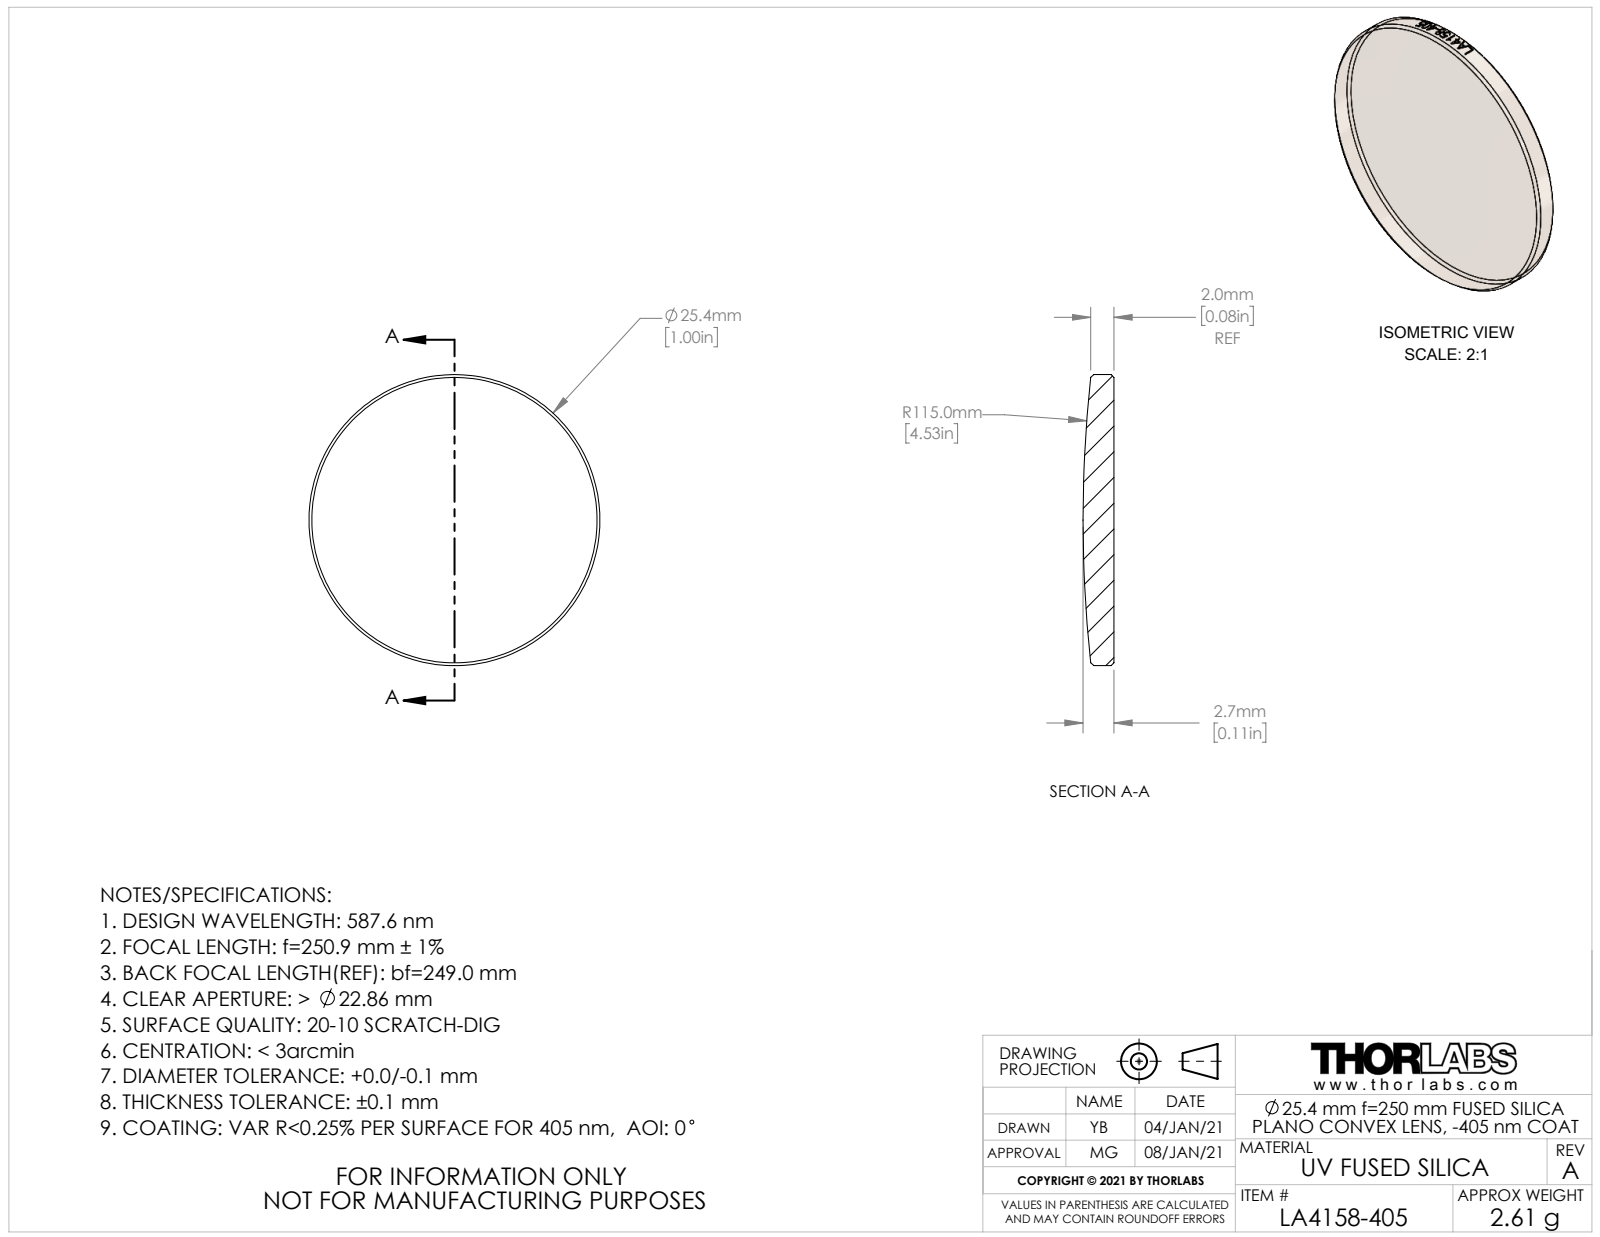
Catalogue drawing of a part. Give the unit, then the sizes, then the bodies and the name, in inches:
Units: inches
Overall size (bounding box): 1 × 1 × 0.106
Round bosses / shafts (diameter × count): ⌀1 ×1
Volume: 0.072 in³ · Surface area: 1.786 in²
Bodies: 1 solid, 30 faces (1 planar, 23 cylindrical, 6 other)
Part name (STEP PRODUCT): CTN016844; CTN016824-E0W
STEP written by: SolidWorks 2018 (AUTOMOTIVE_DESIGN)
